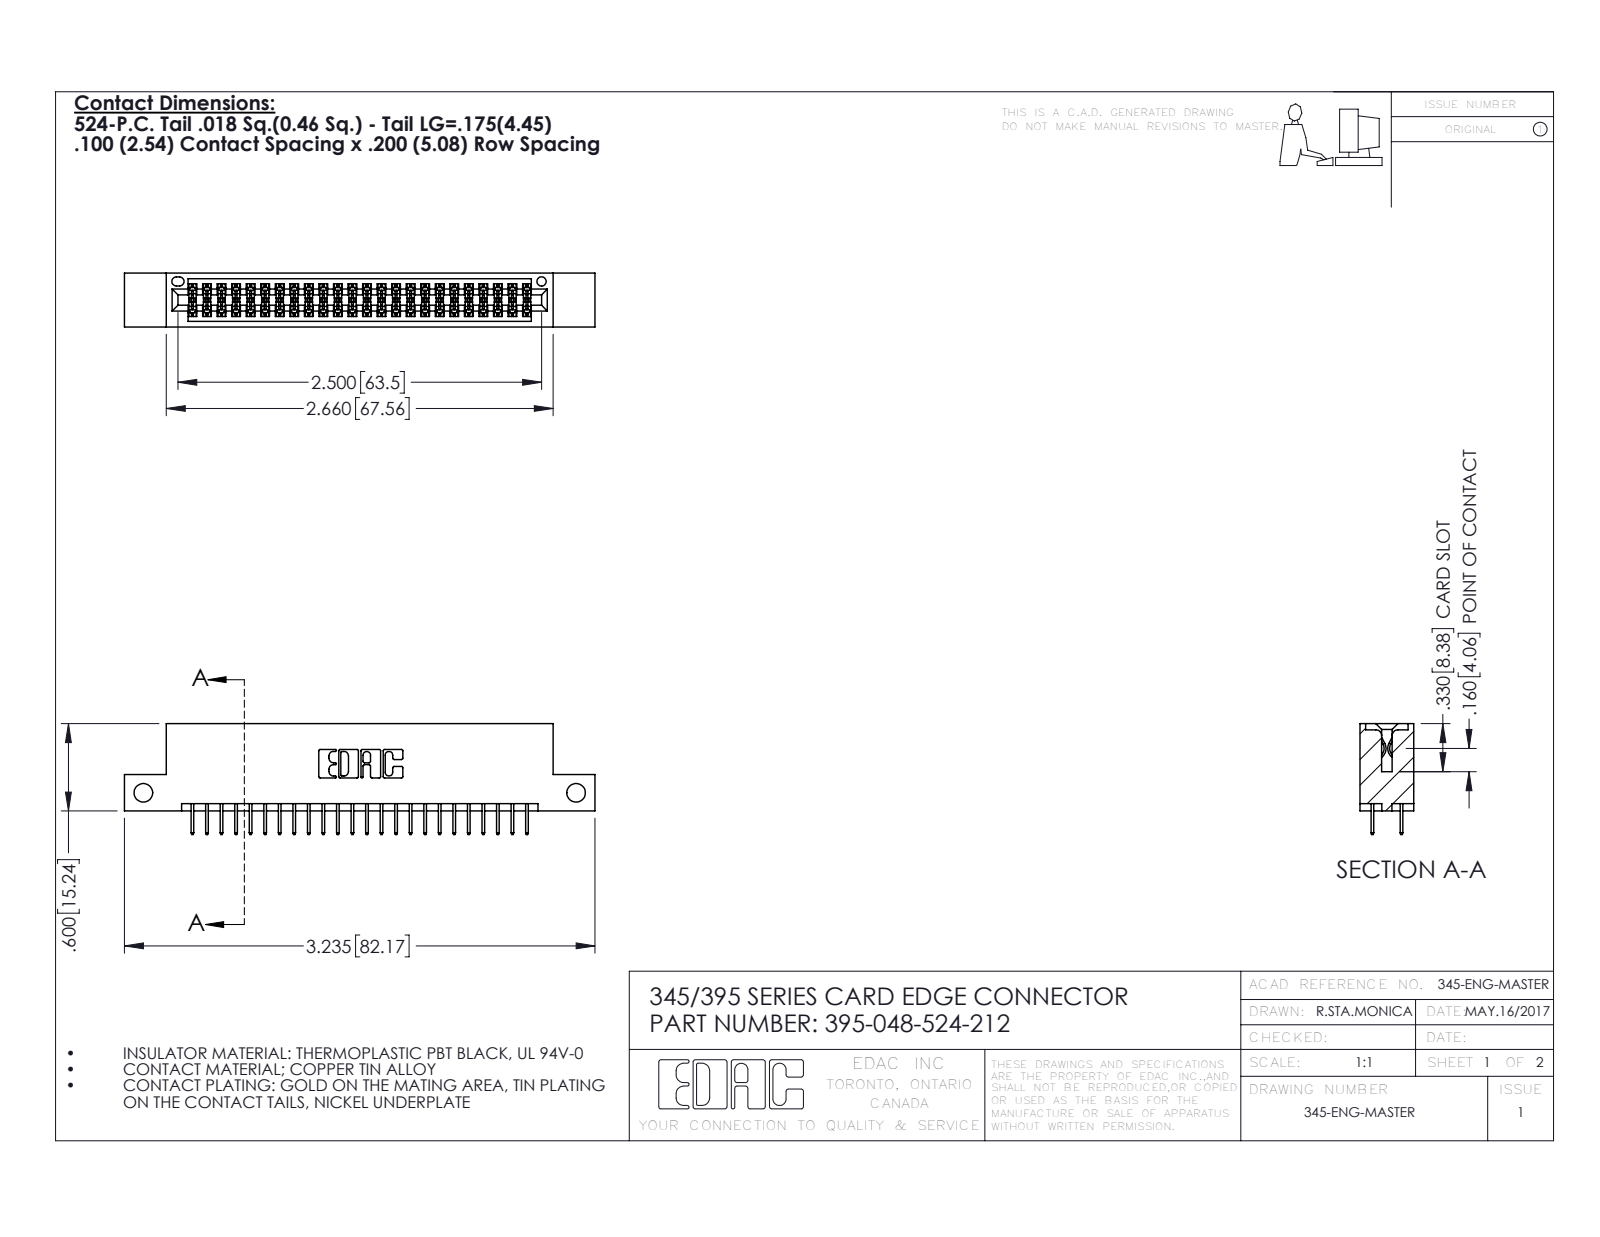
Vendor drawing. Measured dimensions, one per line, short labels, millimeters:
name: 345-292-001_345-293-124; 395-048-524-212; 345 Part_Flush Mounting Lugs - Side Mount
written by: SolidWorks 2016 (CONFIG_CONTROL_DESIGN)
unit: mm
bodies: 49 solids, 2718 faces (1952 planar, 766 cylindrical, 0 other)
size: 82.2 × 19.4 × 9.4
volume: 7 650 mm³; area: 10 640 mm²
holes: 2× ⌀3.3, 1× ⌀1.6
rounds: 72× R0.2, 22× R0.3, 6× R0.2, 6× R0.8, 3× R0.7, 2× R0.4, 2× R0.5, 2× R0.6
face distances: 7.6, 1.8, 5.1, 9.4, 2.5, 6.9, 0.6, 5.7, 1.8, 4.4
hole spacings: 75.6
